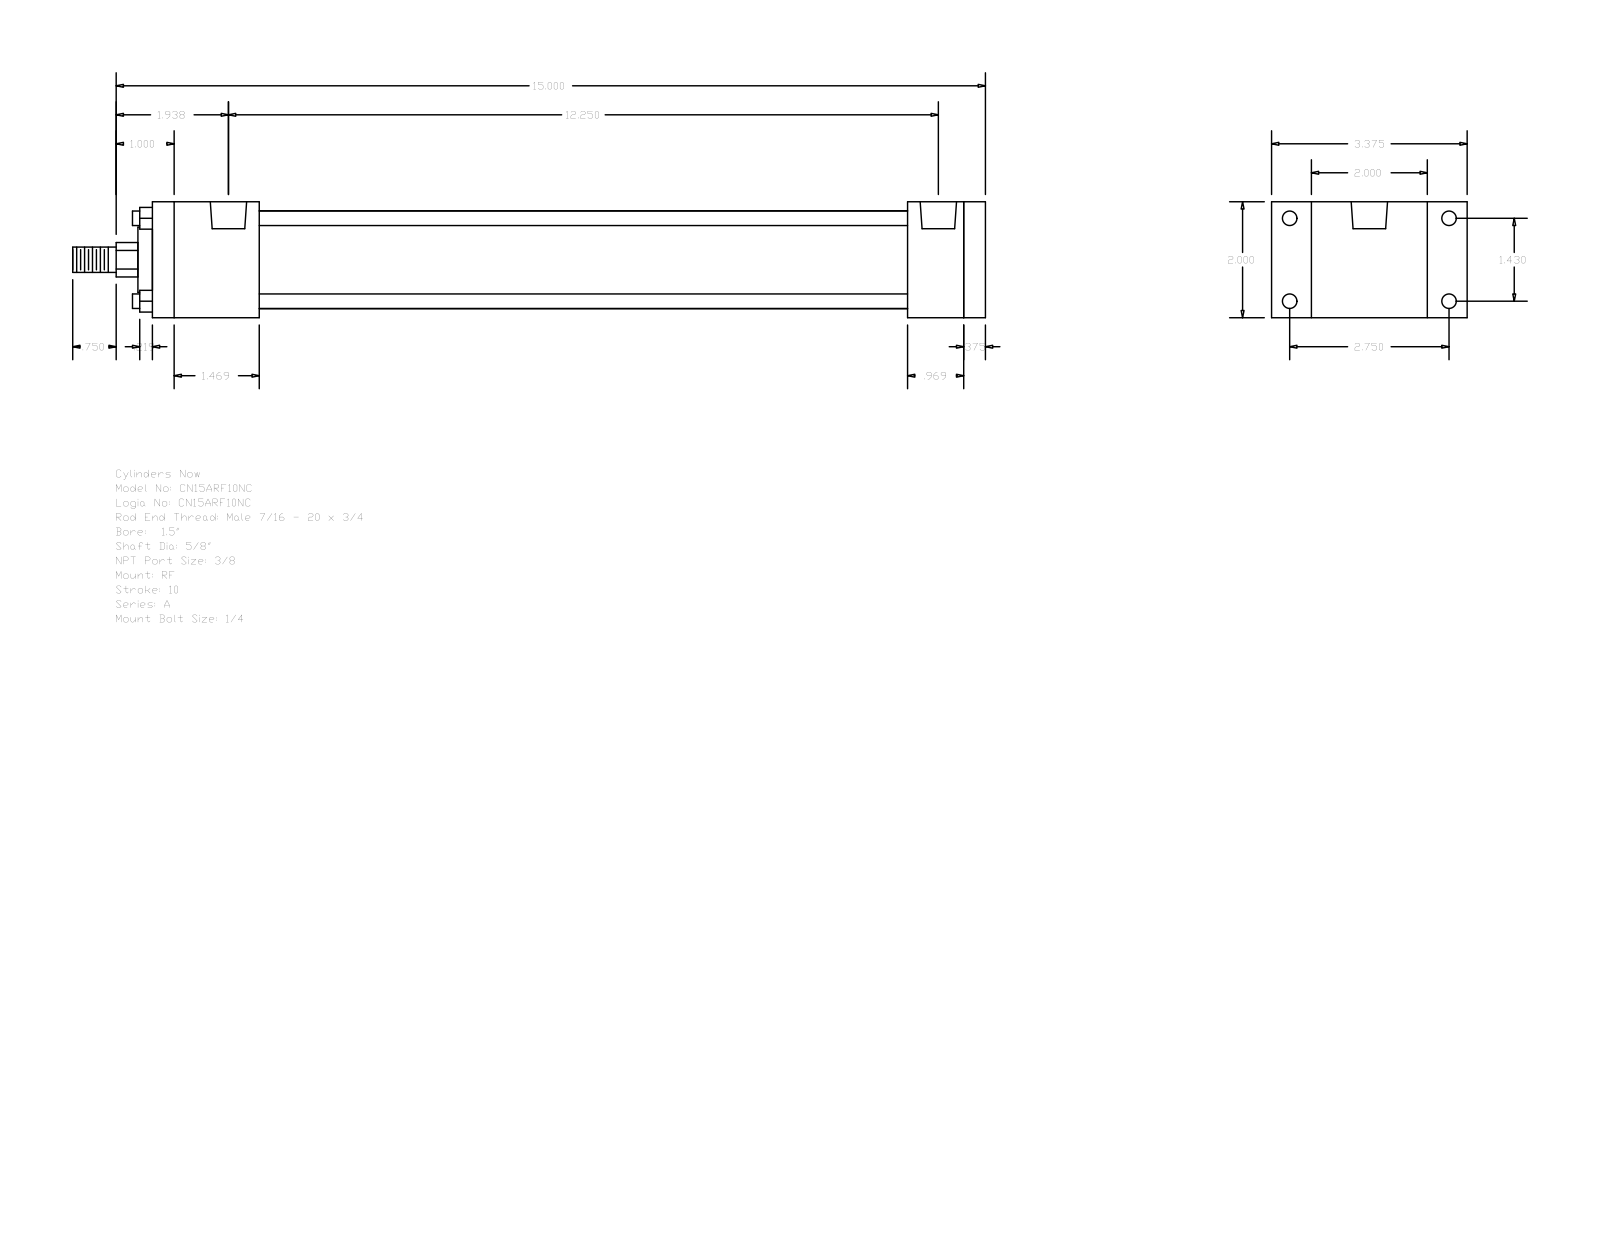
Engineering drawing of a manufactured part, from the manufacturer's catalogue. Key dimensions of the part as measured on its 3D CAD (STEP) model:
Part name (STEP PRODUCT): A_RF__0150_0.625
STEP written by: GSSL Pune (CONFIG_CONTROL_DESIGN)
Units: millimetres
Bodies: 0 solids, 92 faces (64 planar, 28 cylindrical, 0 other)
Overall size (bounding box): 400.05 × 85.72 × 50.8
Round holes (diameter × count): ⌀5.56 ×4, ⌀6.35 ×4, ⌀15.93 ×2
Round bosses / shafts (diameter × count): ⌀6.35 ×4, ⌀42.93 ×1, ⌀28.57 ×1, ⌀15.88 ×1, ⌀11.11 ×1
Partial cylindrical surfaces — rounded edges, fillets, slot ends (radius × count): R7.54 ×1
Main face-to-face distances: 50.8, 9.52, 355.6, 365.12, 330.99, 24.61, 34.13, 46.83, 284.16, 308.77
Hole centre spacings: 3.97, 36.32, 69.84, 78.72, 303.21, 307.18, 311.15
